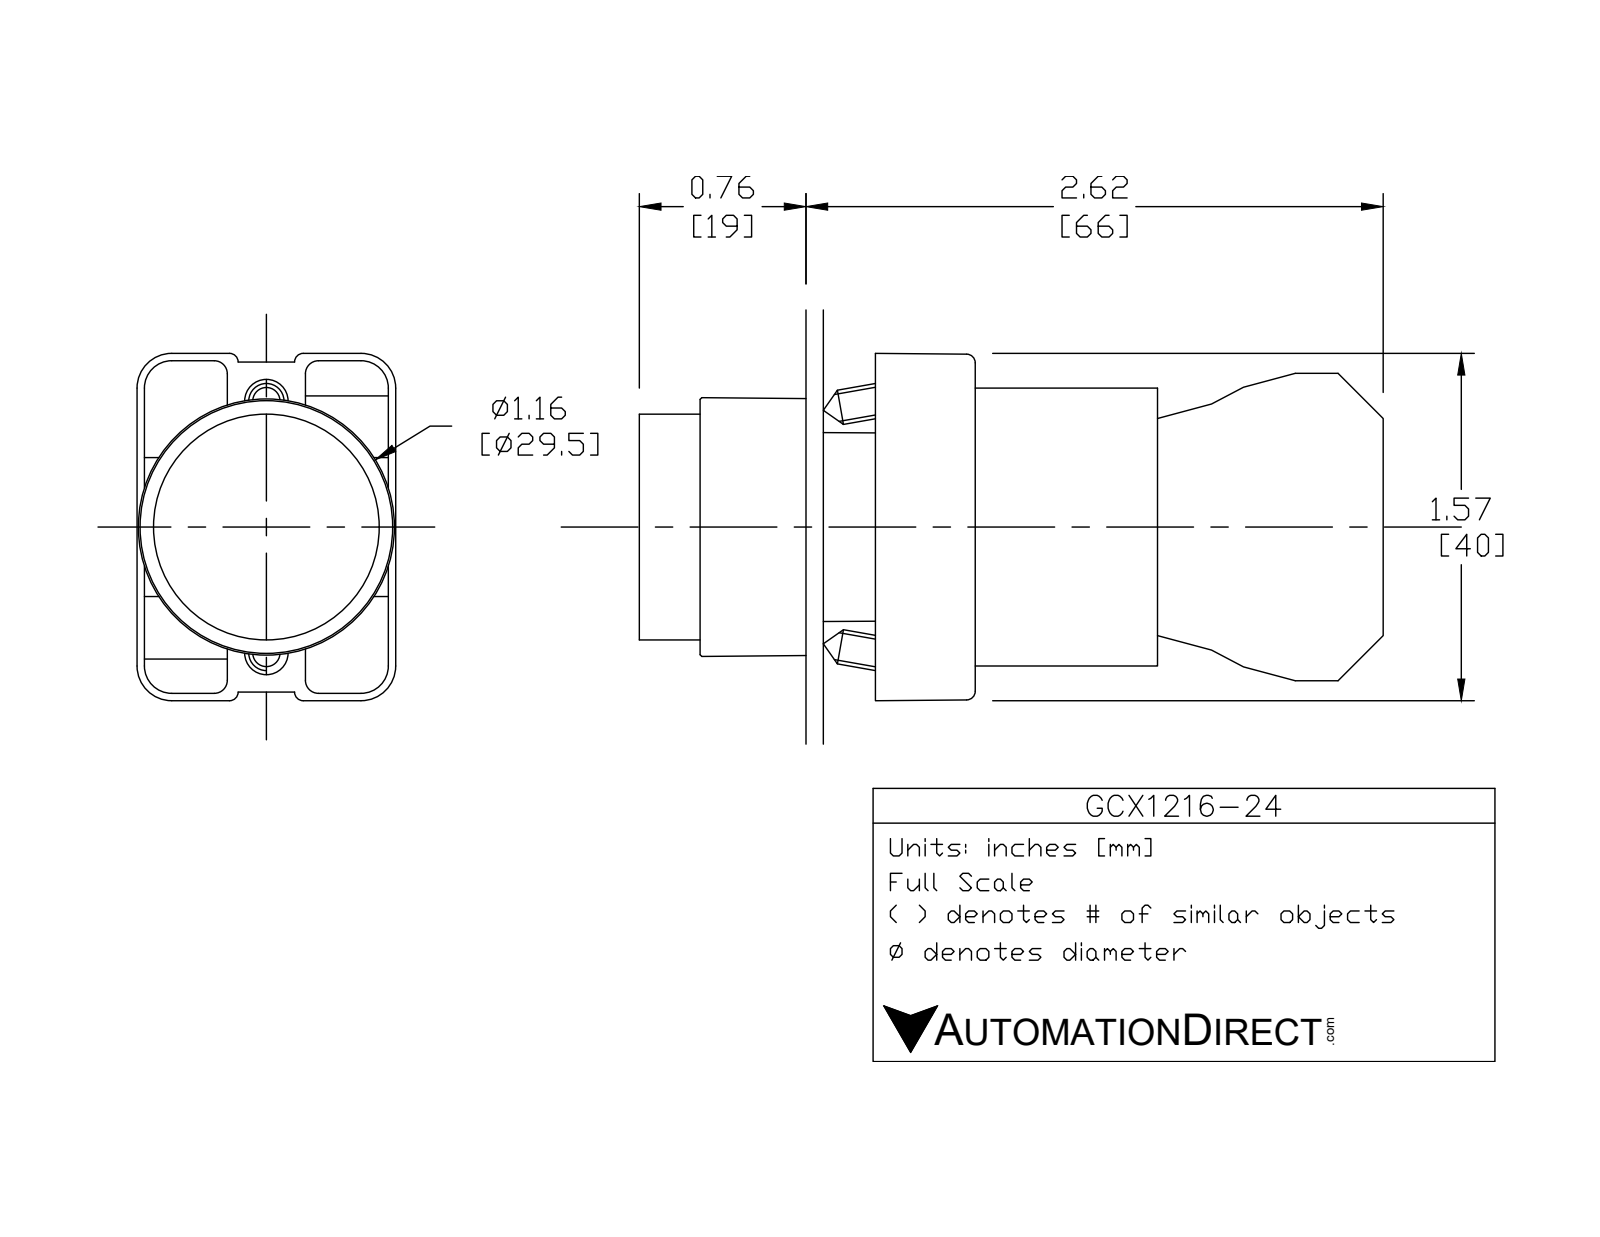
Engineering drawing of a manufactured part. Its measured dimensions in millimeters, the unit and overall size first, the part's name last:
Units: millimetres
Overall size (bounding box): 84.3 × 40.2 × 29.9
Round holes (diameter × count): ⌀2 ×2, ⌀3.1 ×2, ⌀3.3 ×2, ⌀2.2 ×1, ⌀5 ×1, ⌀11.9 ×1, ⌀22.3 ×1, ⌀22.6 ×1, ⌀26 ×1
Round bosses / shafts (diameter × count): ⌀4 ×4, ⌀29.8 ×1, ⌀25.5 ×1, ⌀24 ×1, ⌀21.7 ×1, ⌀19.8 ×1, ⌀12.8 ×1
Partial cylindrical surfaces — rounded edges, fillets, slot ends (radius × count): R1.5 ×24, R1 ×12, R3.1 ×12, R4 ×12, R1 ×8, R3.3 ×2, R0.5 ×1, R1.6 ×1
Main face-to-face distances: 21, 14.7, 29.7, 51.3, 30.3, 0.8, 0.8, 14.6, 29.6, 15.1
Hole centre spacings: 6, 13.8, 12, 12.4
Volume: 44 590 mm³ · Surface area: 23 430 mm²
Bodies: 7 solids, 425 faces (250 planar, 144 cylindrical, 31 other)
Part name (STEP PRODUCT): GCX1216-24; ecx1040; GCX1216 OPERATOR; ecx1029 (+1 more)
STEP written by: SolidWorks 2016 (AUTOMOTIVE_DESIGN)
